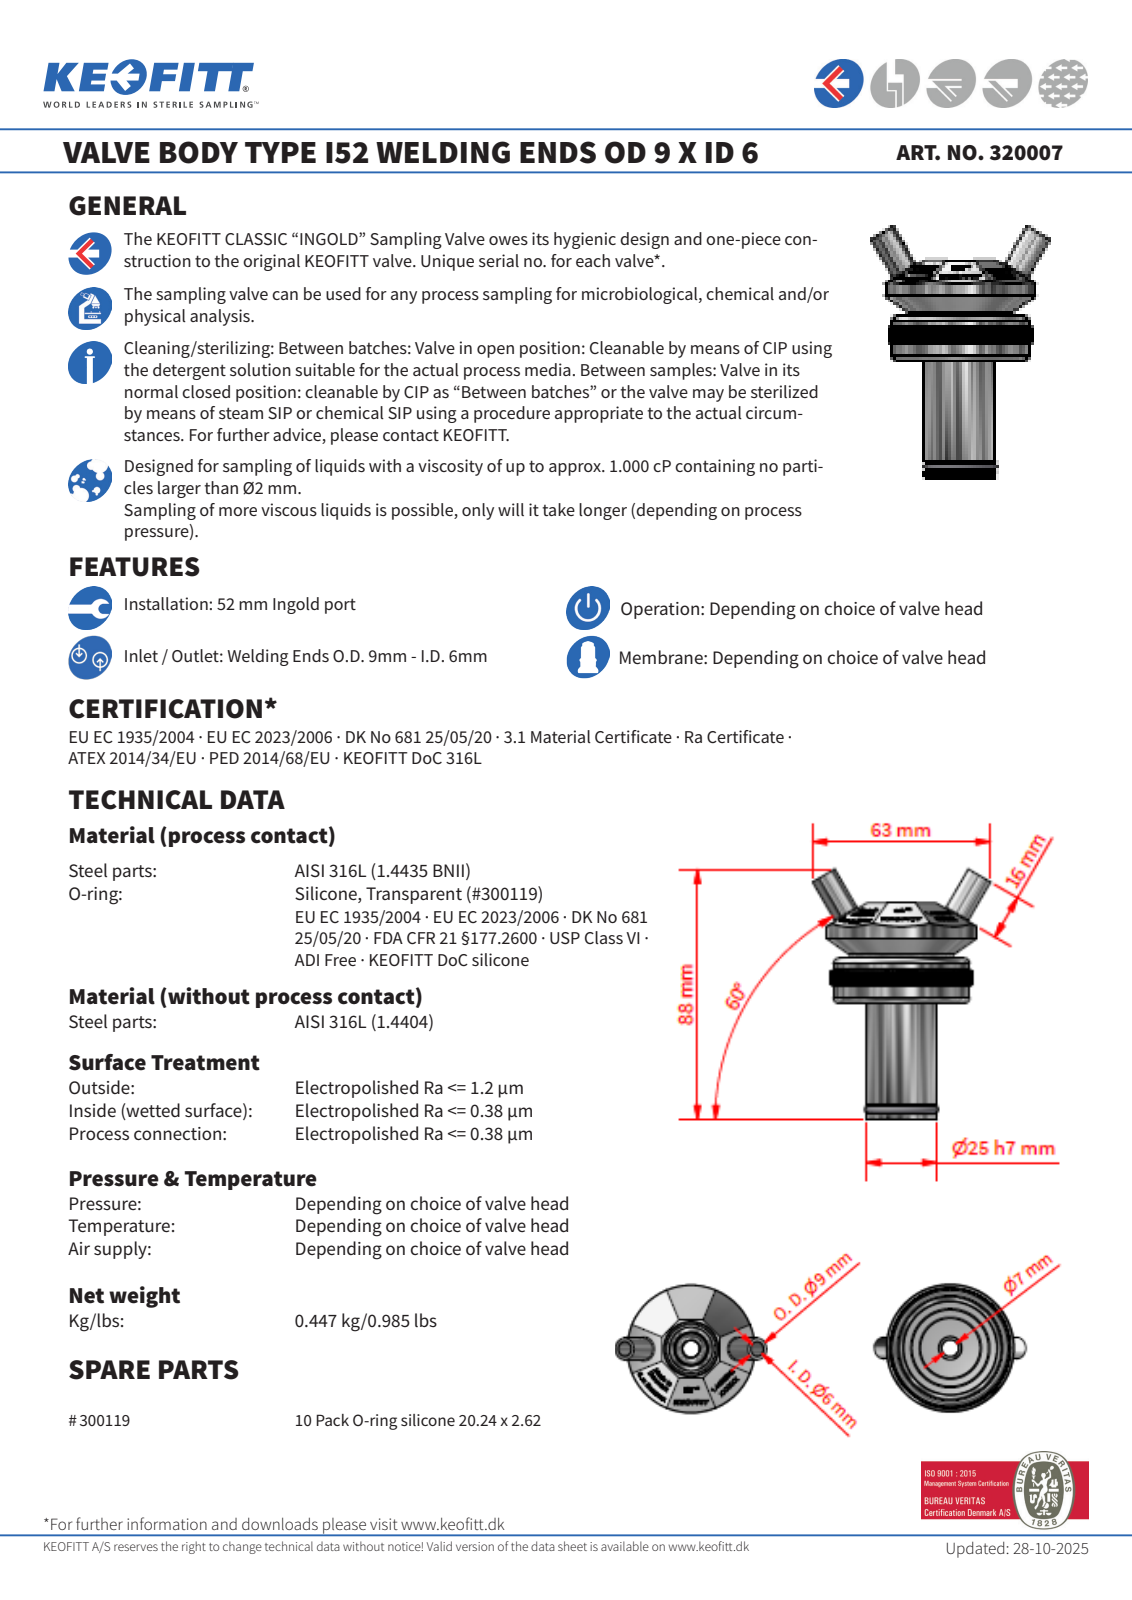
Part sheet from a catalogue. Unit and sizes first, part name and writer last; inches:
Units: inches
Overall size (bounding box): 3.478 × 2.468 × 2.087
Round bosses / shafts (diameter × count): ⌀0.354 ×2, ⌀2.087 ×1, ⌀1.969 ×1, ⌀1.89 ×1, ⌀1.417 ×1, ⌀0.984 ×1, ⌀0.819 ×1
Main face-to-face distances: 0.63, 1.614, 2.244, 3.012, 1.398, 0.768, 0.079, 0.207, 0.128, 1.535
Volume: 4.997 in³ · Surface area: 22.72 in²
Bodies: 2 solids, 36 faces (16 planar, 11 cylindrical, 9 other)
Part name (STEP PRODUCT): 320007
STEP written by: Autodesk Inventor 2022 (AUTOMOTIVE_DESIGN)
